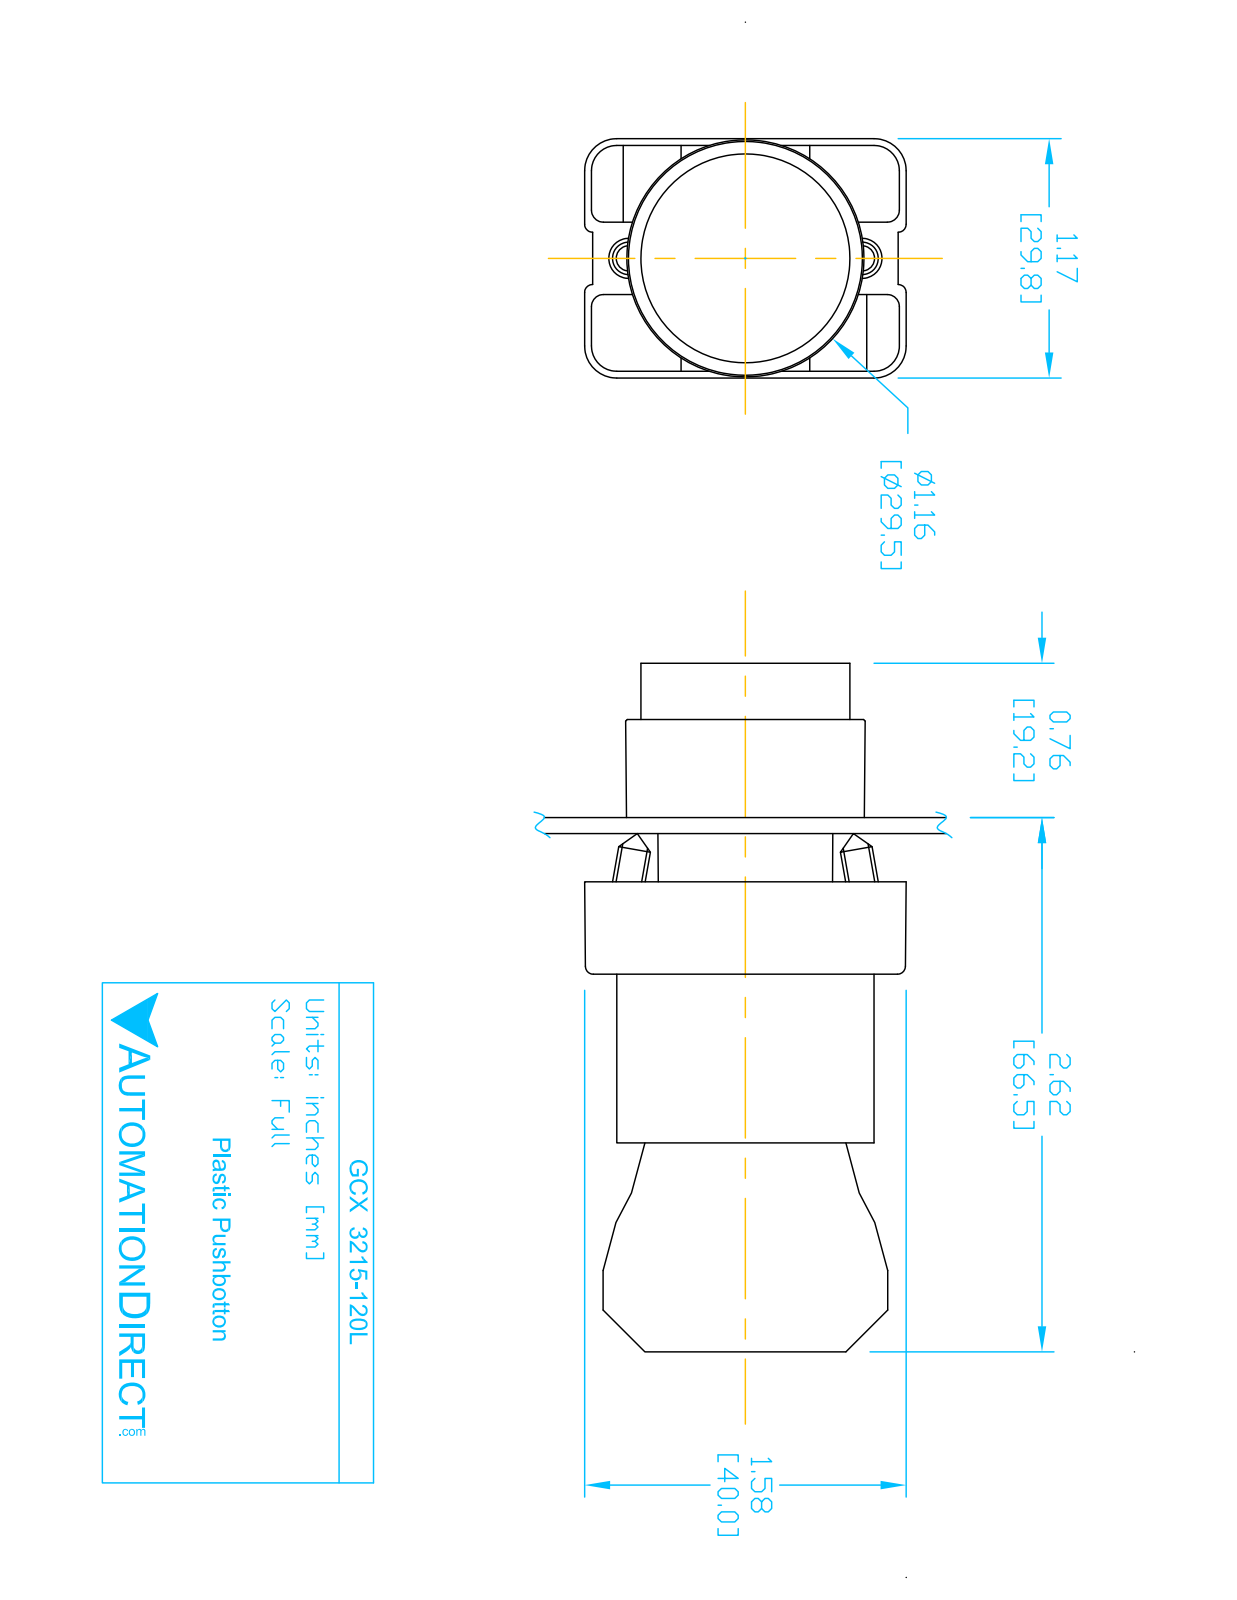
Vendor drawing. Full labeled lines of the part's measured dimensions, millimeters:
Part name (STEP PRODUCT): GCX3215-120L; ECX1050; GCX3215L OPERATOR; ecx1040 (+1 more)
STEP written by: SolidWorks 2016 (AUTOMOTIVE_DESIGN)
Units: millimetres
Bodies: 7 solids, 425 faces (250 planar, 144 cylindrical, 31 other)
Overall size (bounding box): 84.3 × 40.2 × 29.9
Volume: 44 590 mm³ · Surface area: 23 430 mm²
Round holes (diameter × count): ⌀2 ×2, ⌀3.1 ×2, ⌀3.3 ×2, ⌀2.2 ×1, ⌀5 ×1, ⌀11.9 ×1, ⌀22.3 ×1, ⌀22.6 ×1, ⌀26 ×1
Round bosses / shafts (diameter × count): ⌀4 ×4, ⌀29.8 ×1, ⌀25.5 ×1, ⌀24 ×1, ⌀21.7 ×1, ⌀19.8 ×1, ⌀12.8 ×1
Partial cylindrical surfaces — rounded edges, fillets, slot ends (radius × count): R1.5 ×24, R1 ×12, R3.1 ×12, R4 ×12, R1 ×8, R3.3 ×2, R0.5 ×1, R1.6 ×1
Main face-to-face distances: 21, 14.7, 29.7, 51.3, 30.3, 0.8, 0.8, 14.6, 29.6, 15.1
Hole centre spacings: 6, 13.8, 12, 12.4
